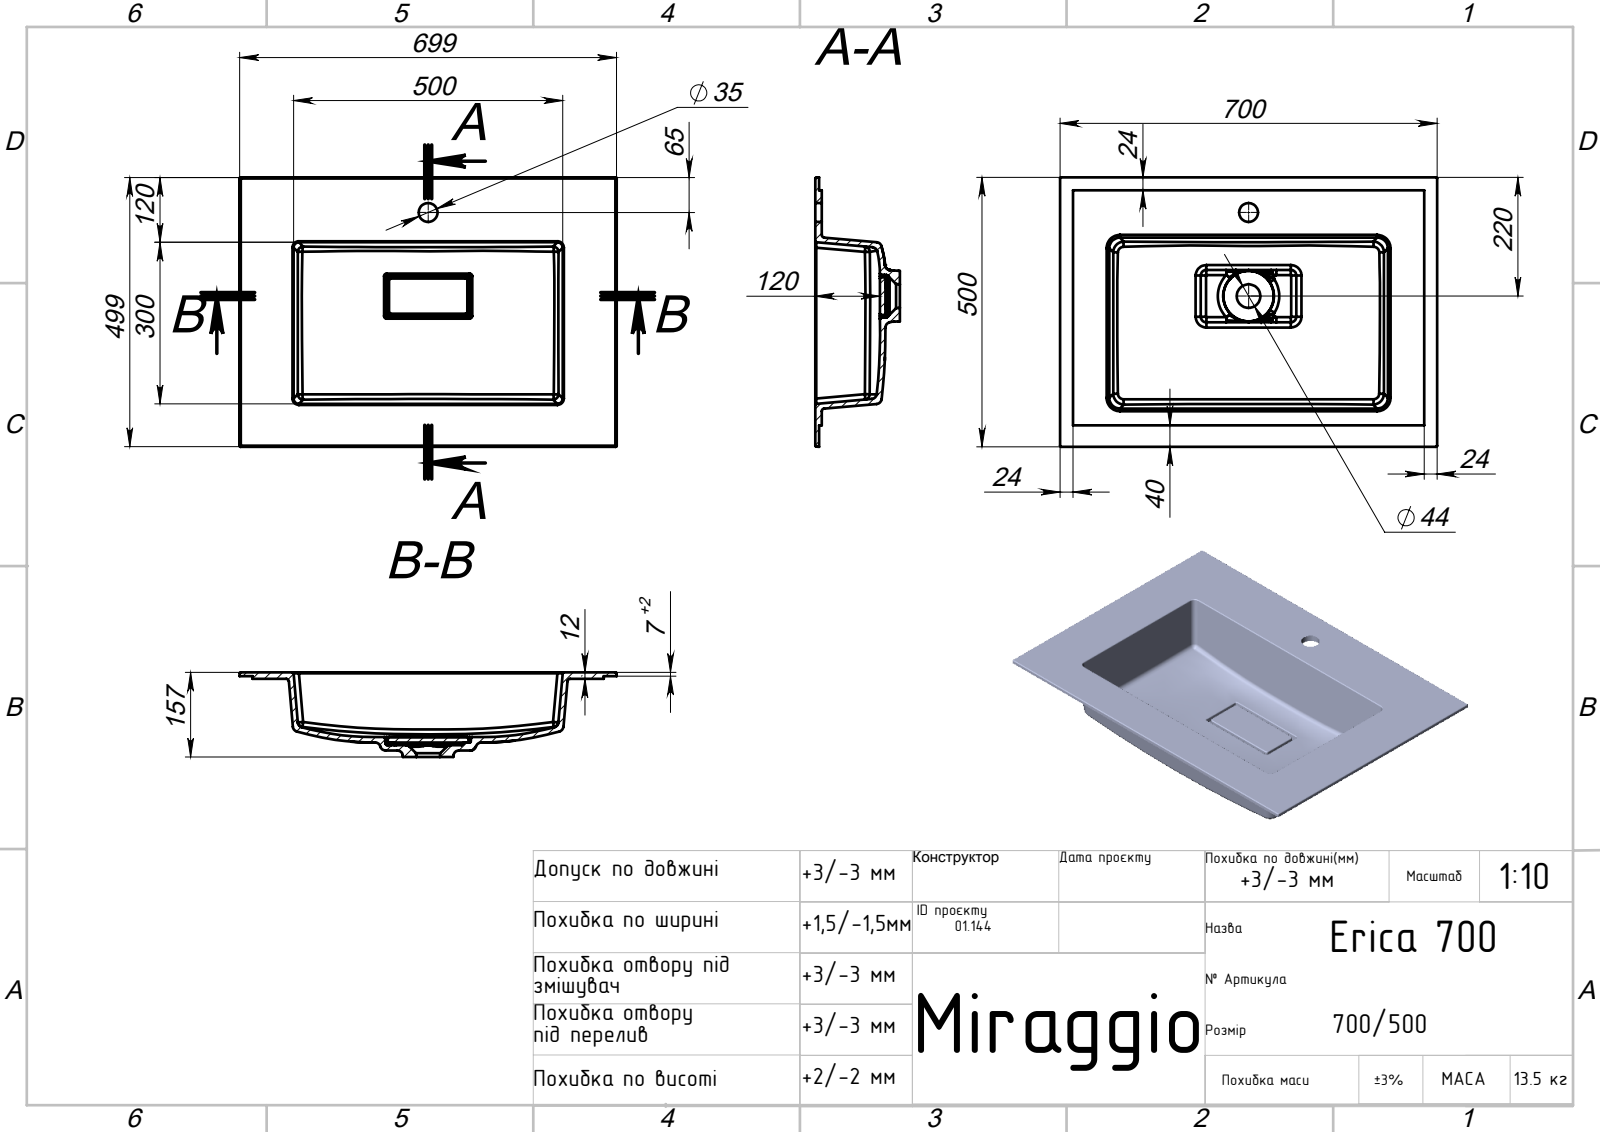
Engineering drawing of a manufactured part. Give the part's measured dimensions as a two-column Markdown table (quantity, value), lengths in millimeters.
| quantity | value |
| --- | --- |
| part name | Erica 700 |
| STEP written by | SolidWorks 2020 (AUTOMOTIVE_DESIGN) |
| units | millimeters |
| bodies | 2 solids, 244 faces (44 planar, 69 cylindrical, 131 other) |
| overall size | 700 × 500 × 157 |
| volume | 5 319 000 mm³ |
| surface area | 1 051 000 mm² |
| round holes (diameter × count) | 35 × 1 |
| partial cylindrical surfaces (radius × count) | 2 × 26, 3 × 18, 6 × 6, 5 × 4, 10 × 4, 20 × 4 |
| main face-to-face distances | 12, 10, 5, 7, 9.99, 123, 118, 130, 108, 113 |
